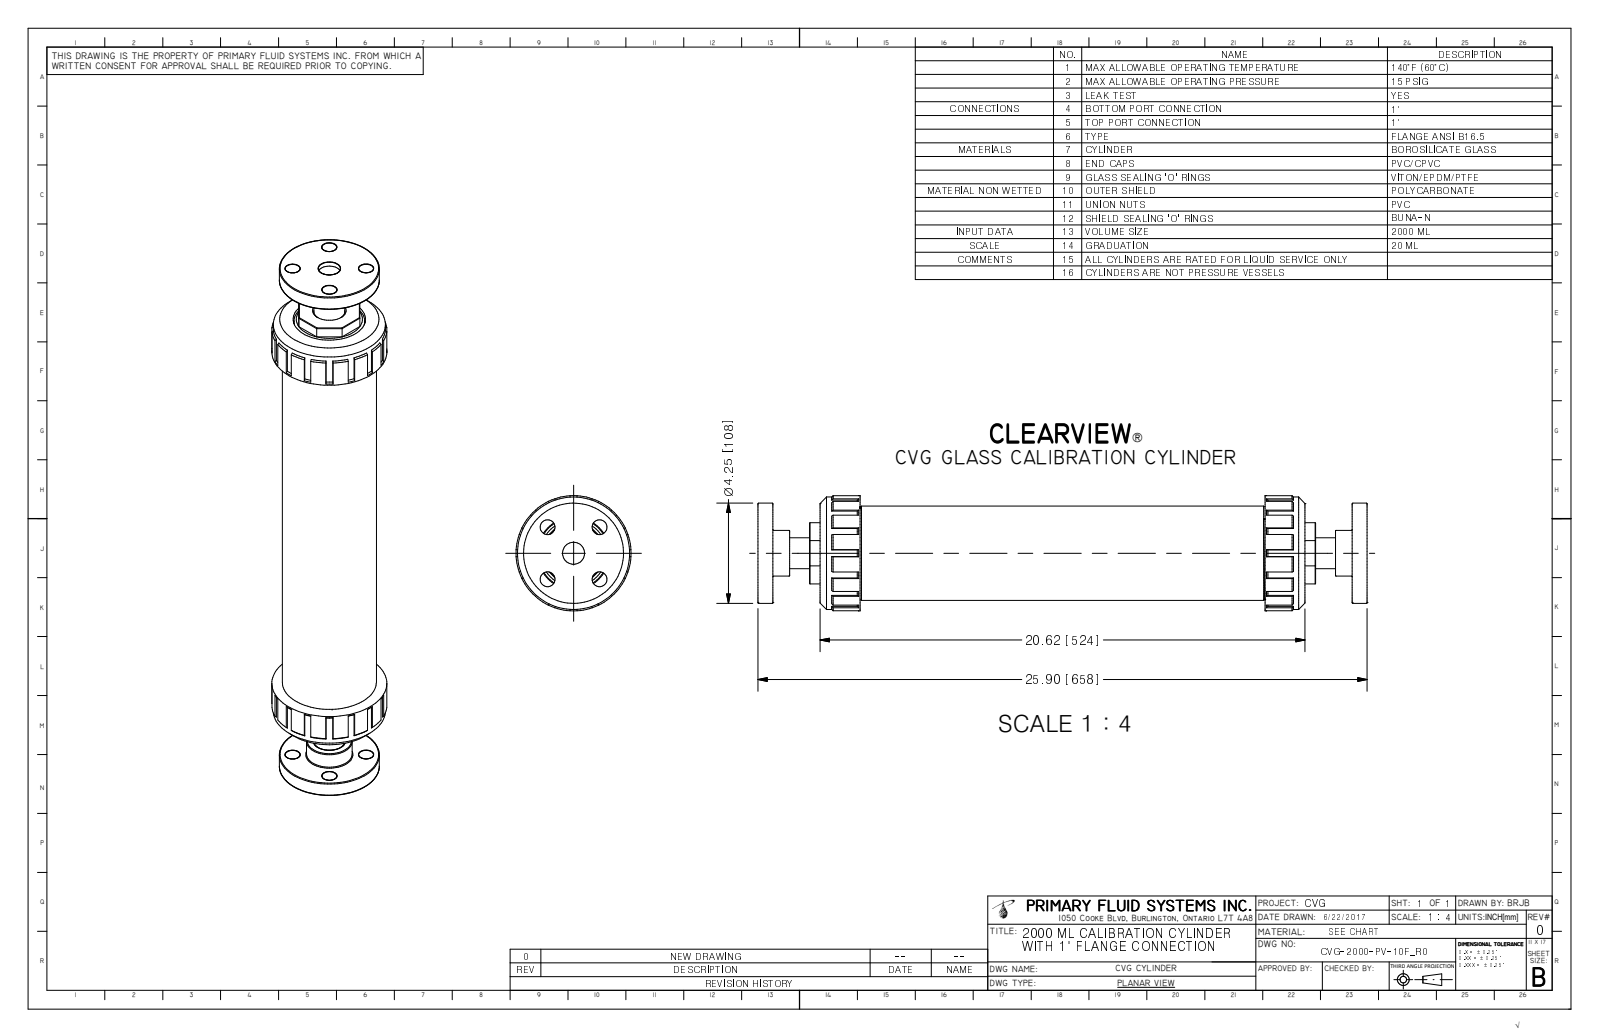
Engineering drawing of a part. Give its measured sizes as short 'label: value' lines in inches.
name: CVG-2000-PV-10F_R0
written by: Autodesk Inventor 2009 (AUTOMOTIVE_DESIGN)
unit: in
bodies: 1 solid, 363 faces (102 planar, 55 cylindrical, 206 other)
size: 25.9 × 4.89 × 4.89
volume: 301.6 in³; area: 478 in²
holes: 4× ⌀0.63, 1× ⌀0.936, 1× ⌀0.957, 1× ⌀3.075, 1× ⌀3.945, 1× ⌀3.945
bosses: 1× ⌀4.89, 1× ⌀4.77, 1× ⌀4.25, 1× ⌀4, 1× ⌀3.819, 1× ⌀3.01, 1× ⌀1.941, 1× ⌀1.315
face distances: 0.635, 25.265, 4.34, 21.56, 3.705, 20.925, 2.64, 23.26, 2.005, 22.625
hole spacings: 1.562, 2.209, 3.125
